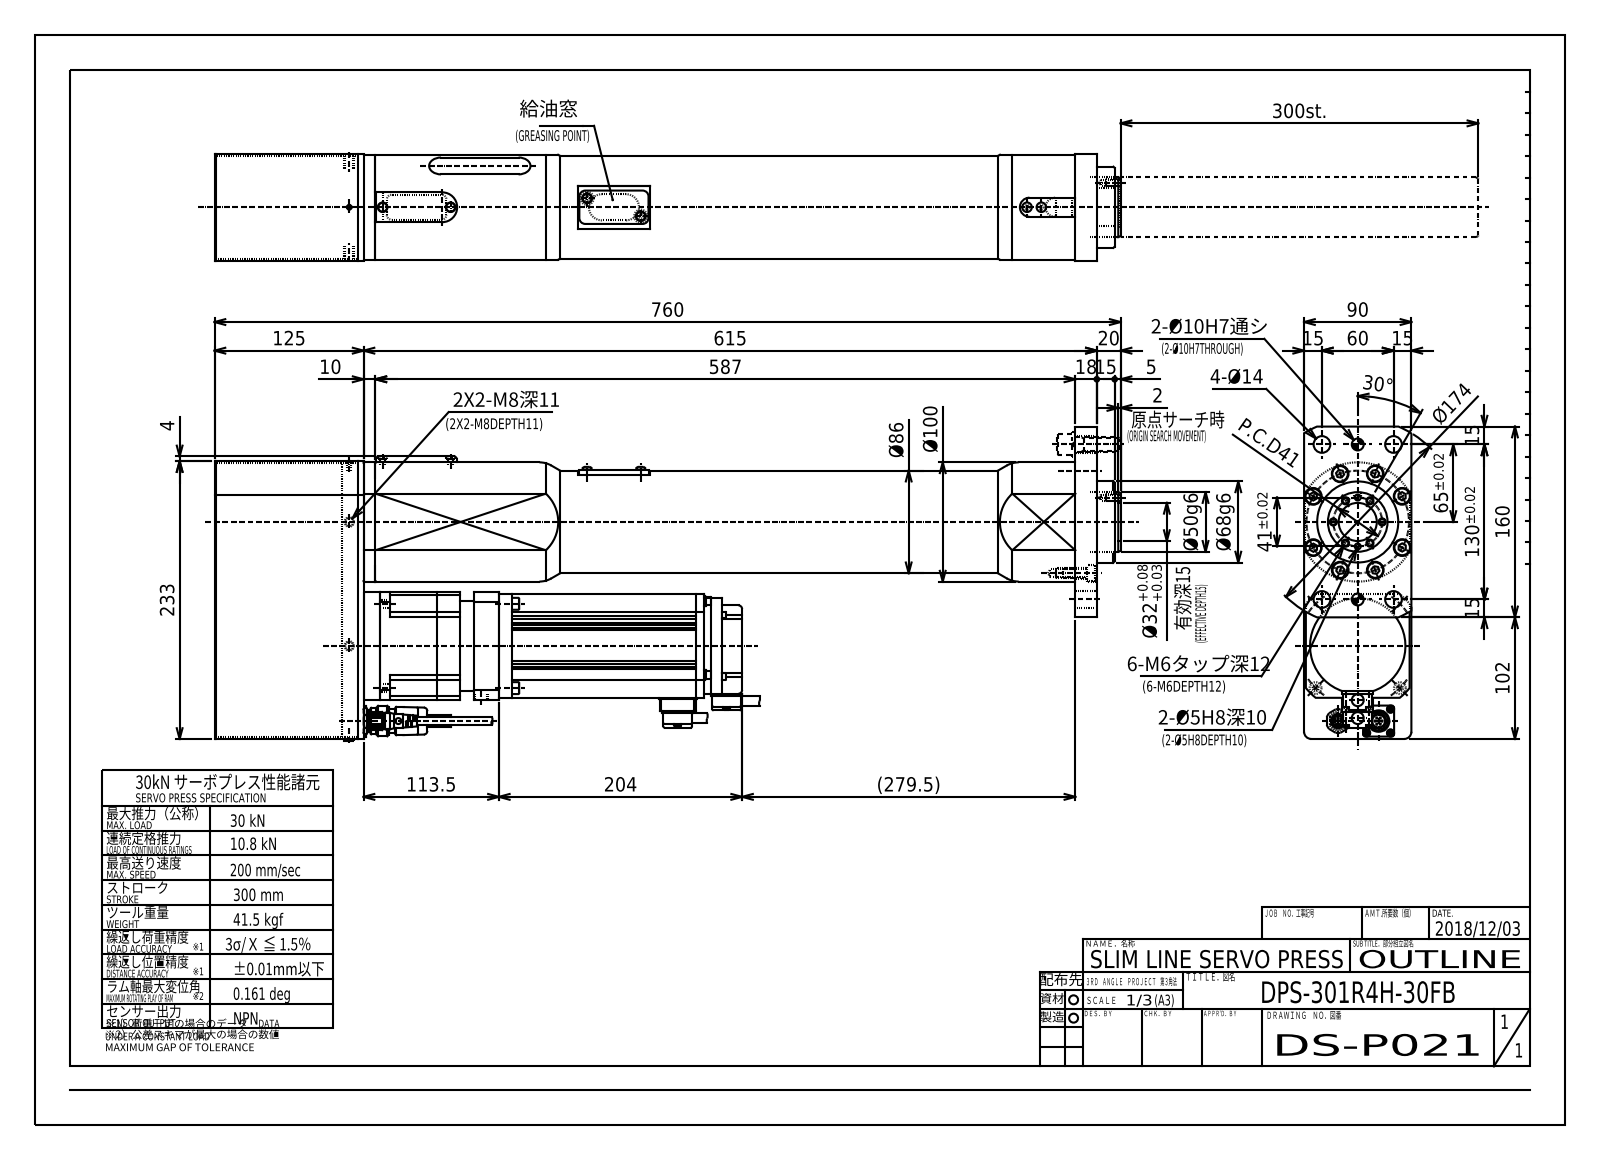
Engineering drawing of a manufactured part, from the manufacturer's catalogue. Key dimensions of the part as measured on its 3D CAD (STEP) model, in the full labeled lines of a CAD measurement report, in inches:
Part name (STEP PRODUCT): DPS-301R4H-30FB(DS-P021)_OUTLINE; DS-P021-01_OUTLINE
STEP written by: Autodesk Inventor 2017 (AUTOMOTIVE_DESIGN)
Units: inches
Bodies: 2 solids, 1406 faces (793 planar, 392 cylindrical, 221 other)
Overall size (bounding box): 29.921 × 10.374 × 3.543
Volume: 512.1 in³ · Surface area: 1 068 in²
Round holes (diameter × count): ⌀0.551 ×12, ⌀0.194 ×10, ⌀0.354 ×8, ⌀0.217 ×4, ⌀0.315 ×4, ⌀0.097 ×2, ⌀0.197 ×2, ⌀0.262 ×2, ⌀0.394 ×2, ⌀0.128 ×1, ⌀0.157 ×1, ⌀0.335 ×1
Round bosses / shafts (diameter × count): ⌀0.315 ×12, ⌀0.512 ×8, ⌀0.276 ×6, ⌀0.197 ×6, ⌀0.394 ×5, ⌀0.346 ×4, ⌀0.295 ×4, ⌀0.236 ×4
Partial cylindrical surfaces — rounded edges, fillets, slot ends (radius × count): R0.039 ×50, R0.079 ×32, R0.012 ×16, R0.157 ×15, R0.197 ×12, R0.118 ×11, R0.02 ×10, R0.128 ×8
Main face-to-face distances: 3.543, 0.059, 0.039, 3.504, 3.484, 3.445, 3.425, 0.02, 0.591, 0.65
Hole centre spacings: 1.693, 0.807, 1.073, 2.426, 3.182, 1.128, 1.14, 1.158
